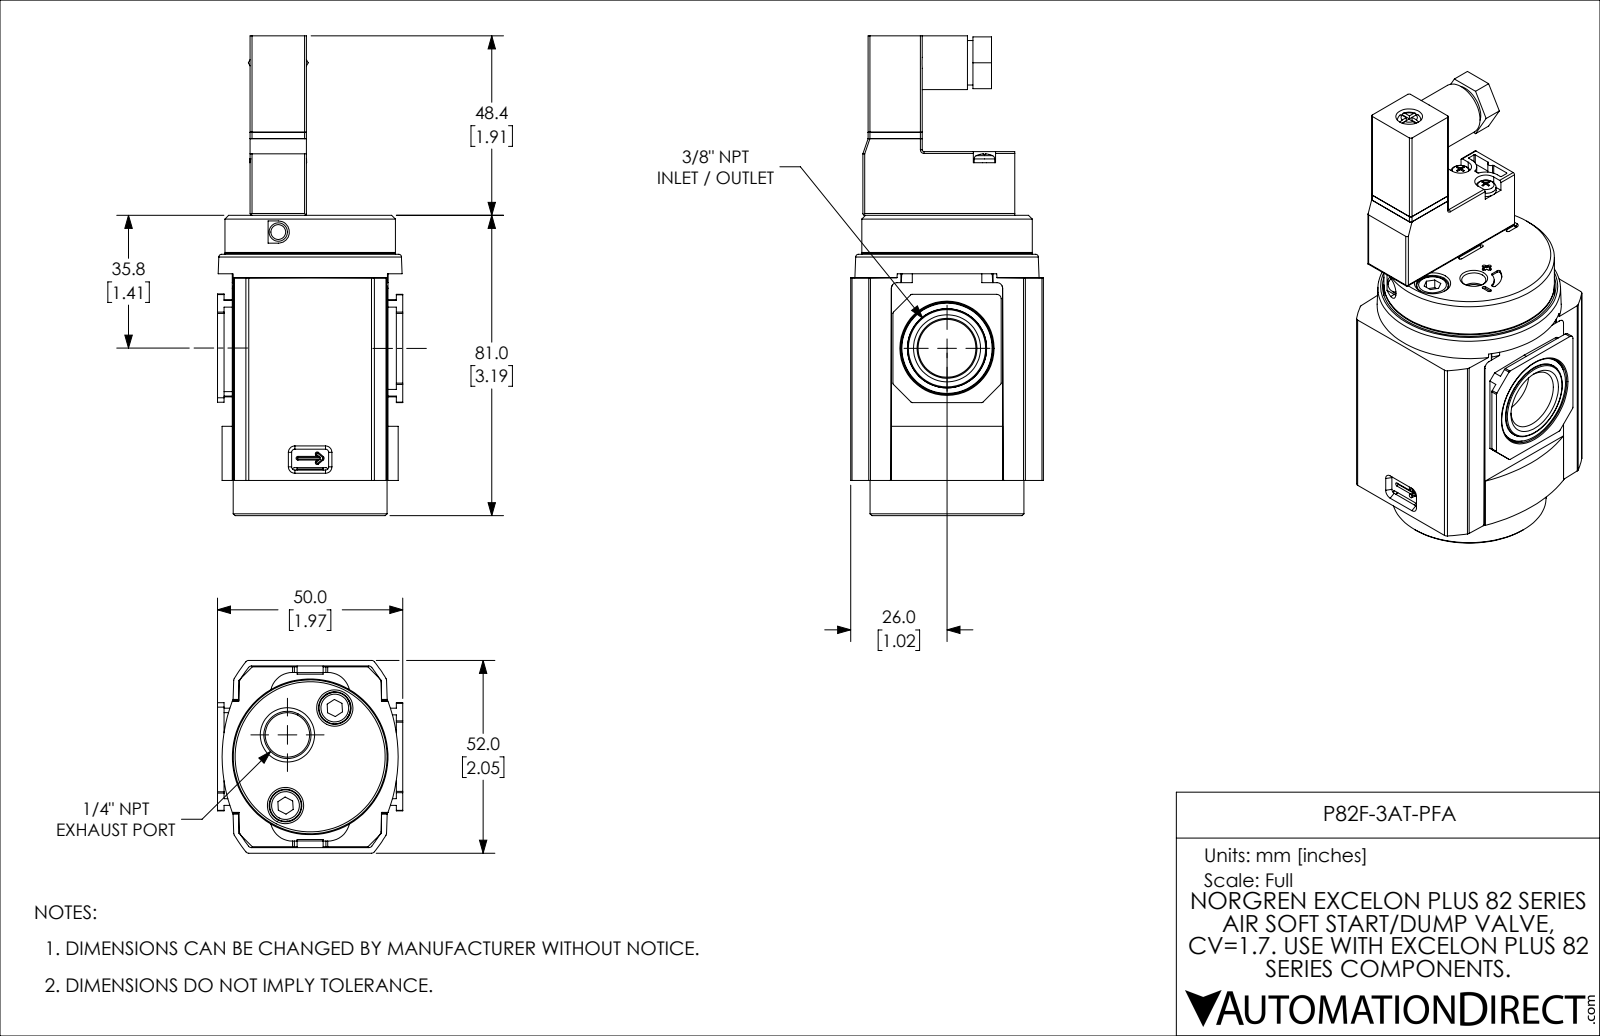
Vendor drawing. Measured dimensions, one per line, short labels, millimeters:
name: P82F-3AT-PFA
written by: SolidWorks 2021 (CONFIG_CONTROL_DESIGN)
unit: mm
bodies: 7 solids, 857 faces (385 planar, 249 cylindrical, 223 other)
size: 129.4 × 52 × 50
volume: 174 182 mm³; area: 58 139 mm²
holes: 4× ⌀4.13, 4× ⌀5.3, 4× ⌀8.8, 3× ⌀1.5, 3× ⌀2.46, 3× ⌀8.5, 2× ⌀0.8, 2× ⌀3.1, 1× ⌀3.15, 1× ⌀3.8, 1× ⌀6.5, 1× ⌀6.8
bosses: 4× ⌀5, 2× ⌀8.5, 2× ⌀3, 1× ⌀46, 1× ⌀41.5, 1× ⌀39.8, 1× ⌀37, 1× ⌀14.5
rounds: 47× R0.5, 18× R0.25, 16× R1, 4× R1.2, 4× R3, 4× R6, 2× R0.1, 2× R1.25
face distances: 1.75, 1.5, 50.5, 50.25, 48.75, 10, 49.5, 59.5, 52, 49
hole spacings: 3.8, 5.05, 5.41, 7.11, 14.74, 16.69, 24.88, 25.36
